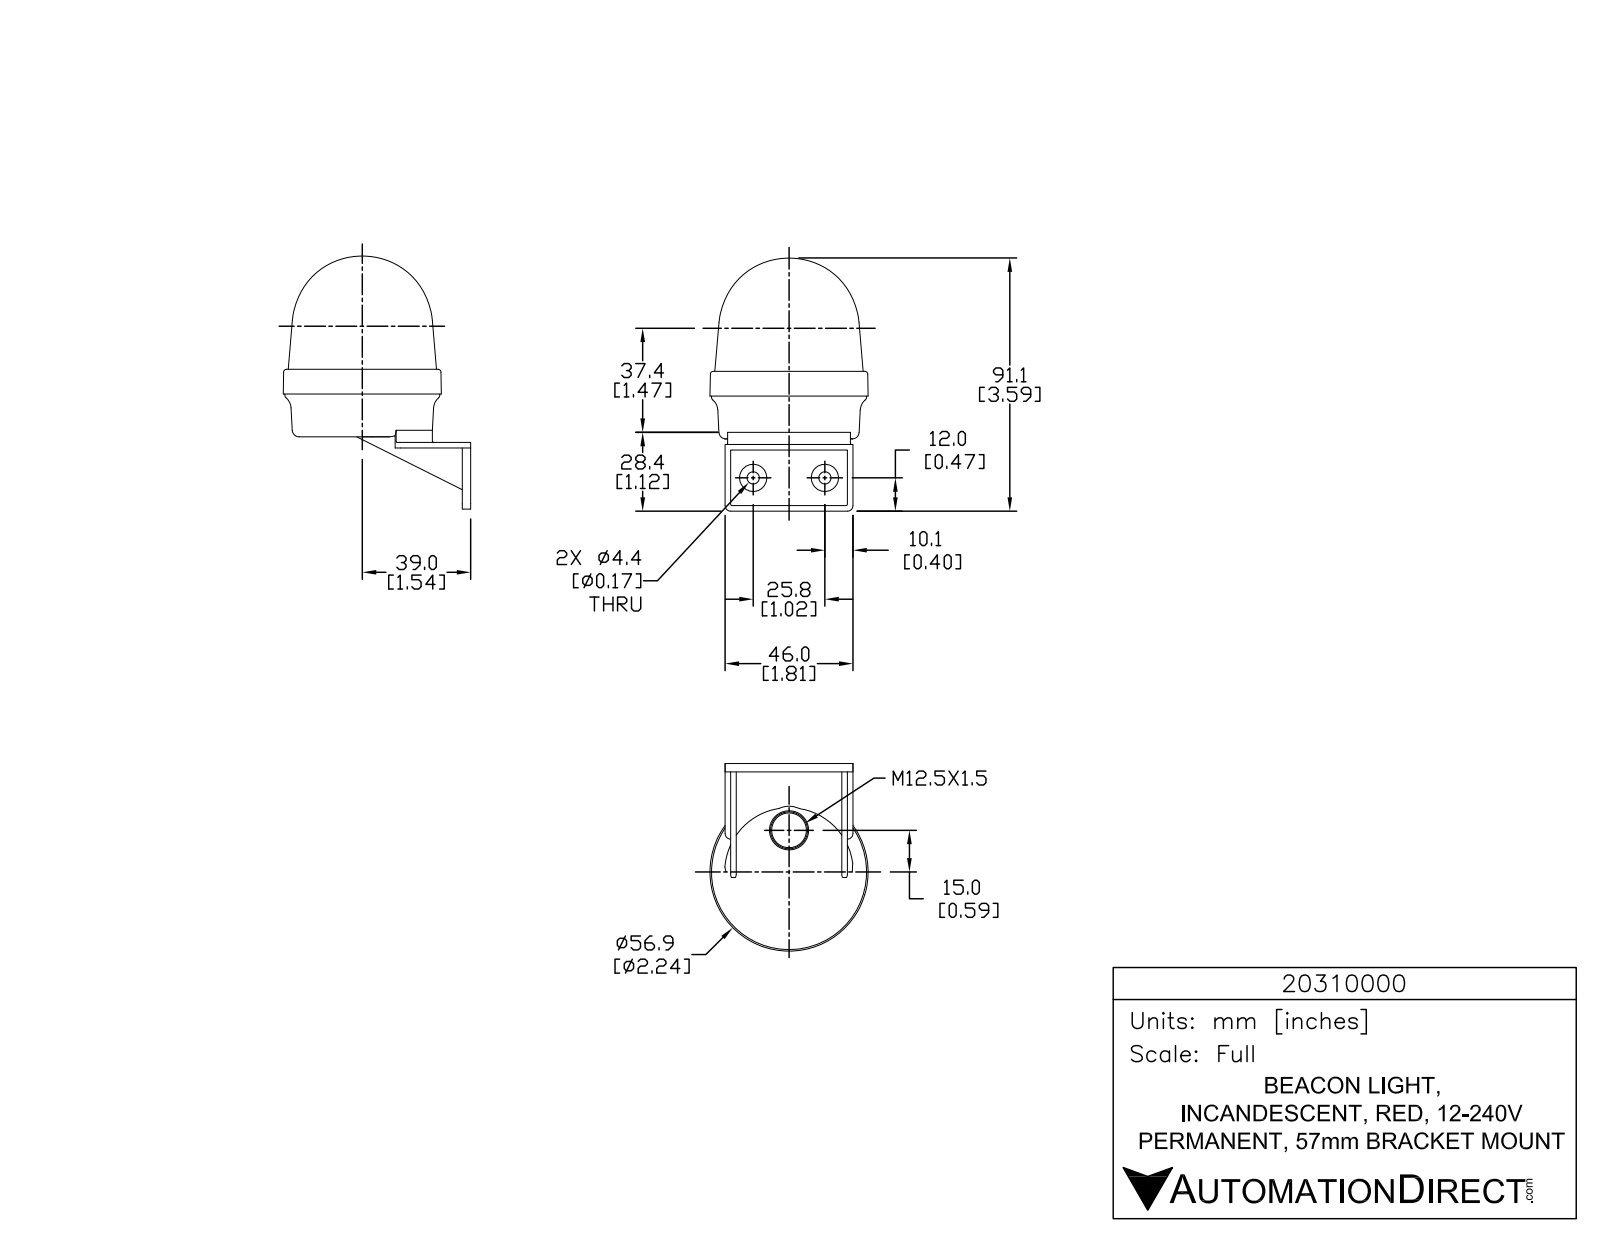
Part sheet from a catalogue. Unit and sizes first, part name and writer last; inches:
Units: inches
Overall size (bounding box): 3.587 × 2.837 × 2.392
Round holes (diameter × count): ⌀0.039 ×3, ⌀0.173 ×2
Round bosses / shafts (diameter × count): ⌀0.226 ×3, ⌀0.056 ×3, ⌀0.386 ×2, ⌀2.197 ×1
Partial cylindrical surfaces — rounded edges, fillets, slot ends (radius × count): R0.008 ×6, R0.008 ×6, R0.008 ×6, R0.02 ×6, R0.131 ×6, R0.079 ×4, R0.004 ×3, R0.005 ×3
Main face-to-face distances: 0.079, 0.157, 1.575, 1.654, 0.039, 0.118, 1.496, 0.866, 0.945, 1.733
Hole centre spacings: 1.016
Volume: 7.74 in³ · Surface area: 28.71 in²
Bodies: 1 solid, 813 faces (550 planar, 169 cylindrical, 94 other)
Part name (STEP PRODUCT): 20310000
STEP written by: SolidWorks 2015 (AUTOMOTIVE_DESIGN)
